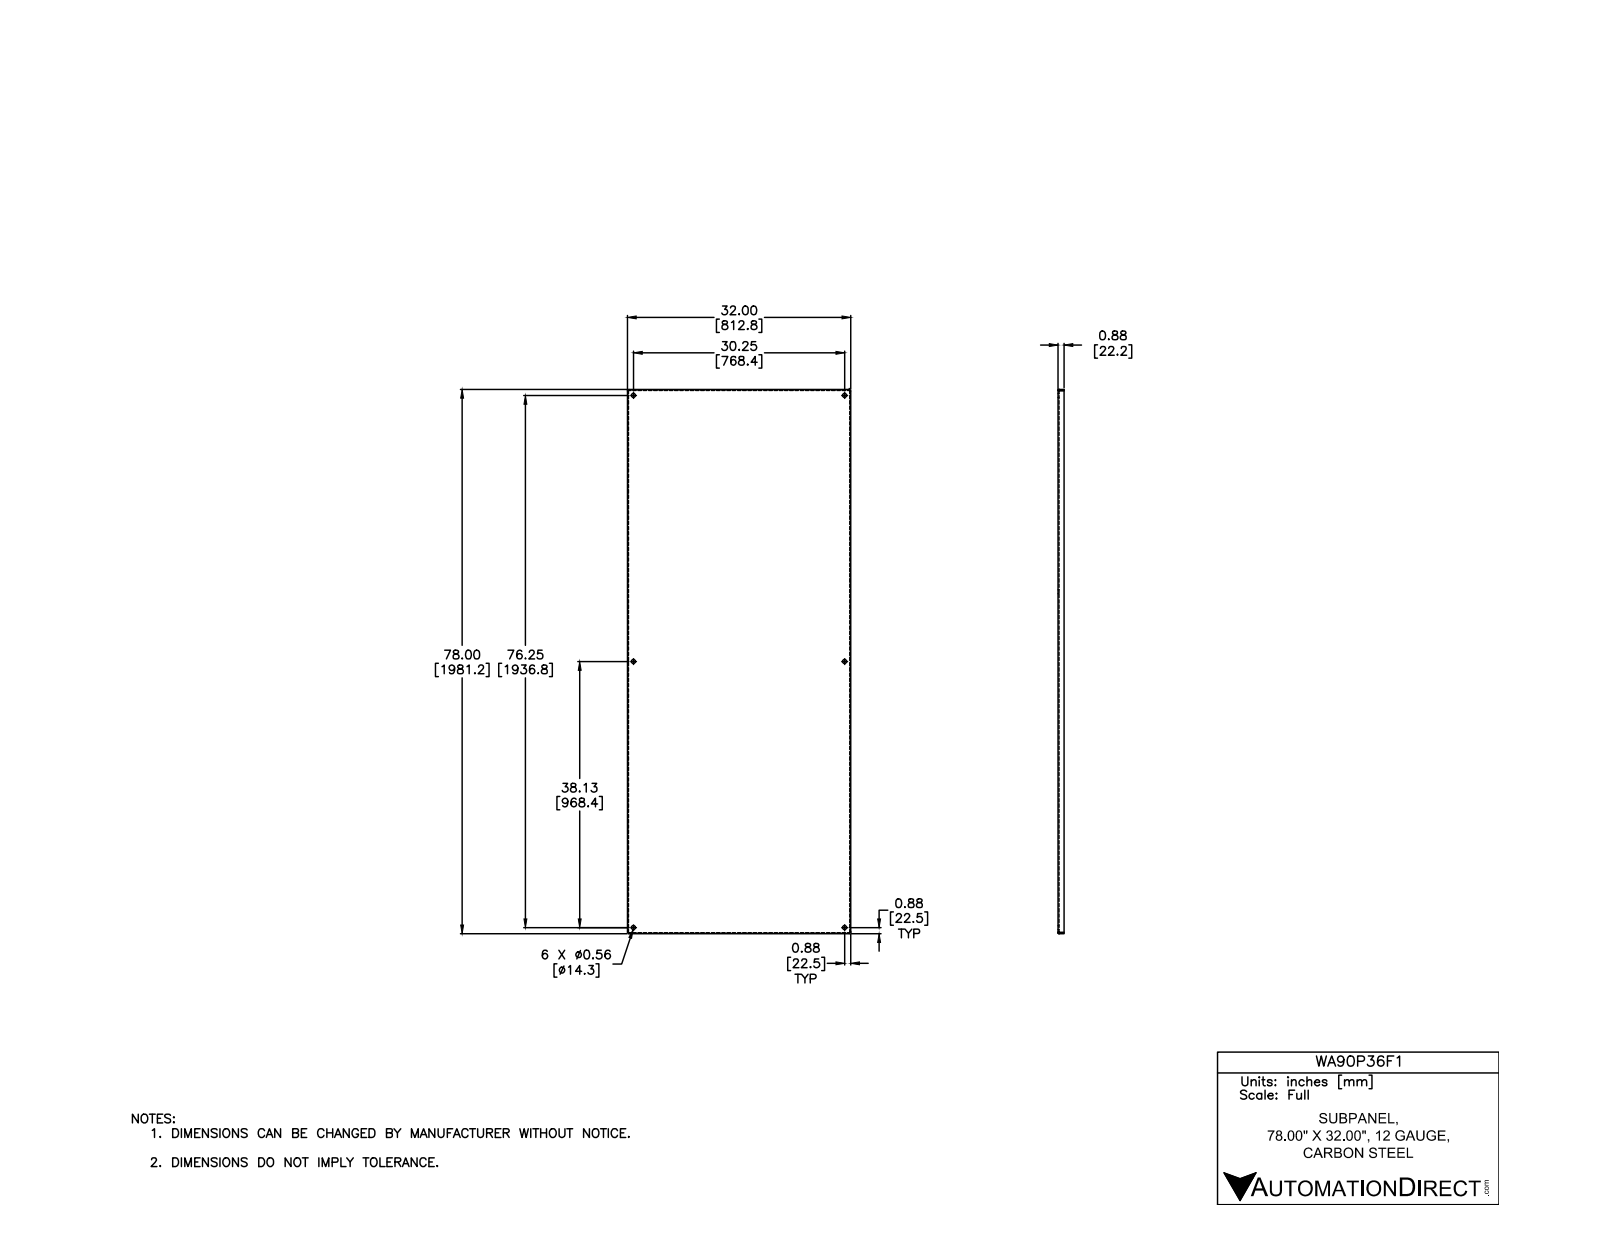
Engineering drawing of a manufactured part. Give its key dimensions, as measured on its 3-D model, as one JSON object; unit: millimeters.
{"part_name": "WA_P_F", "step_written_by": "Autodesk Inventor 2012 (AUTOMOTIVE_DESIGN)", "units": "millimeters", "bodies": {"solids": 1, "faces": 44, "planar": 22, "cylindrical": 14, "other": 8}, "overall_size": [1981.2, 812.8, 22.2], "volume_mm3": 4084000, "surface_area_mm2": 3444000, "round_holes": [[14.3, 6]], "partial_cylinders_radius": [[0.8, 4], [3.2, 4]], "face_to_face_distances": [2.4, 810.4, 812.8, 808.1, 1978.8, 1981.2, 1976.5, 19.8, 22.2, 4.1], "hole_center_spacings": [768.4, 968.4, 968.4, 1236.2, 1236.2, 1936.8, 2083.6]}
